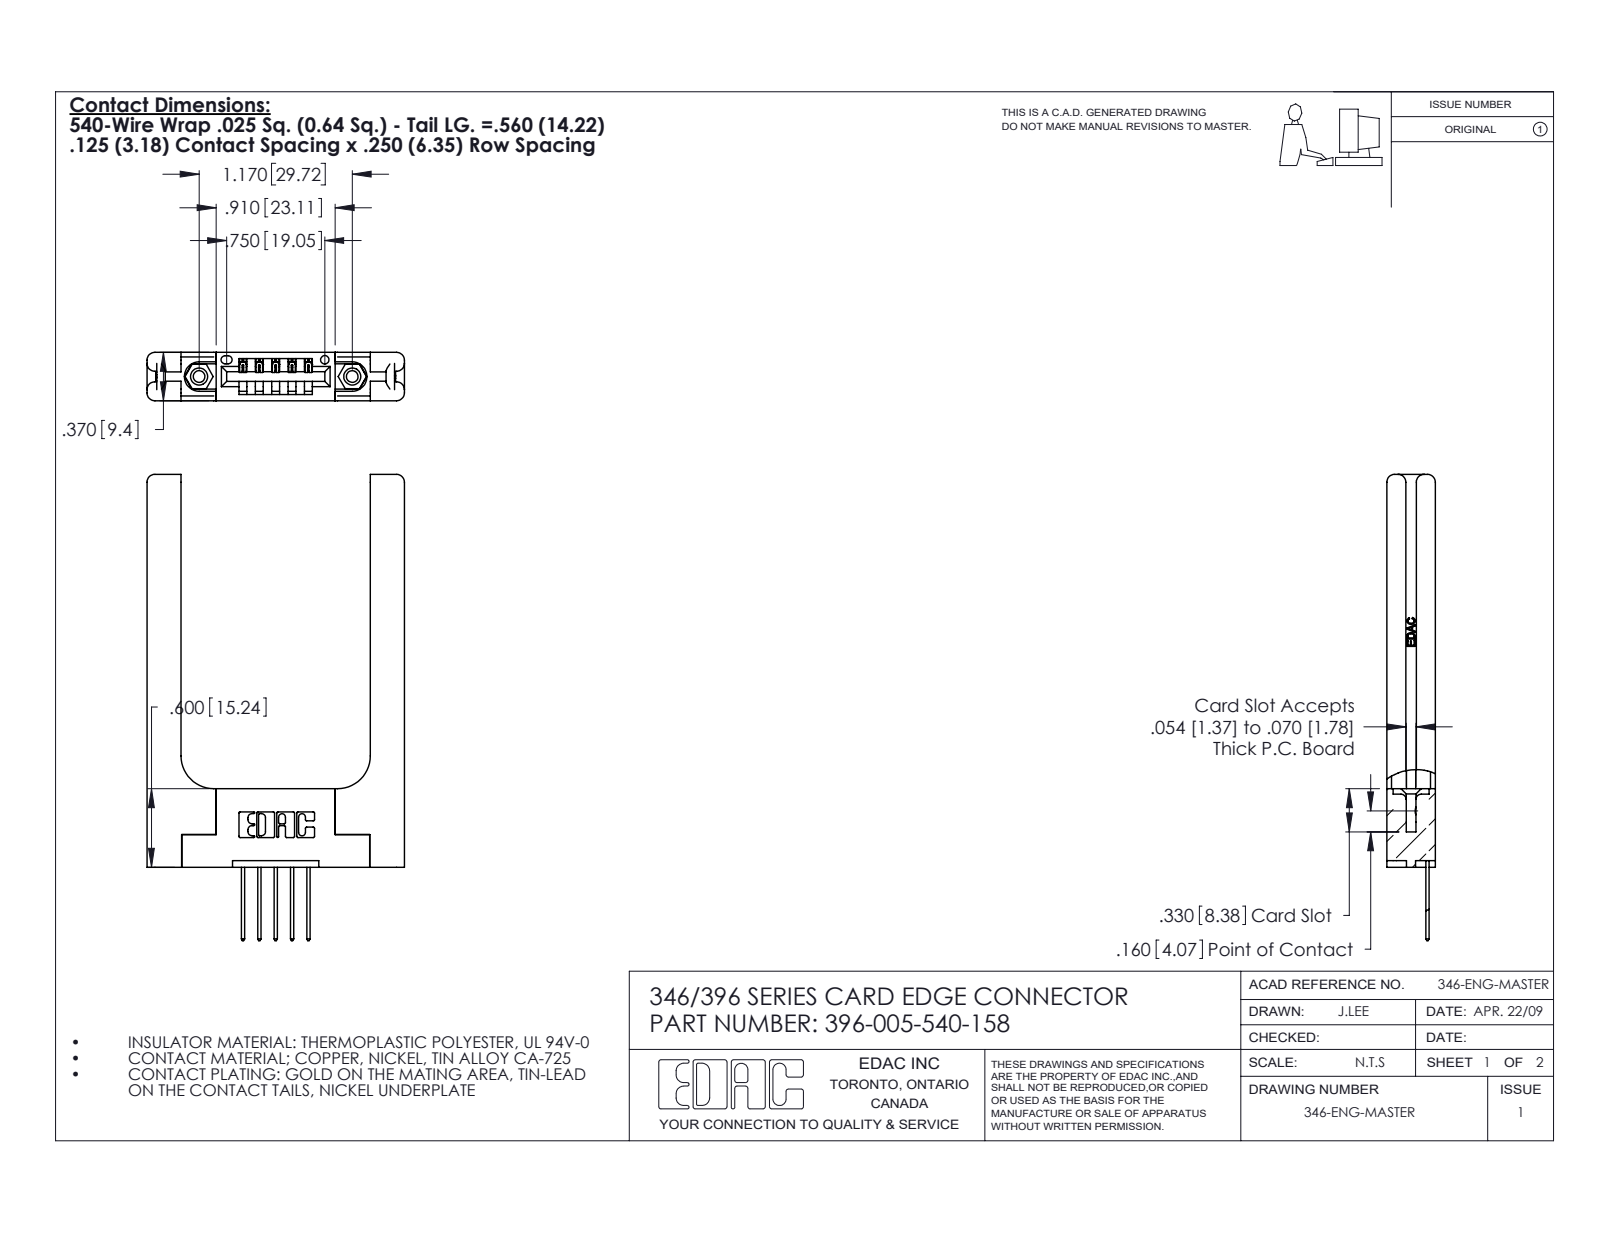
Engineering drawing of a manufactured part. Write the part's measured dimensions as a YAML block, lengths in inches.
part_name: "345-292-001_345-293-140; 346 Part_Flush Mounting Lugs - 0.156 Dia-TH; 346-220-058_345-220-058; 396-005-540-158 (+1 more)"
step_written_by: "SolidWorks 2020 (CONFIG_CONTROL_DESIGN)"
units: inches
bodies: {solids: 10, faces: 682, planar: 438, cylindrical: 184, other: 60}
overall_size: [3.56, 1.966, 0.37]
volume: 0.734
surface_area: 16.27
round_holes:
  - {diameter: 0.089, count: 2}
  - {diameter: 0.125, count: 2}
  - {diameter: 0.156, count: 2}
  - {diameter: 0.064, count: 1}
round_bosses_or_shafts:
  - {diameter: 0.155, count: 2}
partial_cylinders:
  - {radius: 0.01, count: 22}
  - {radius: 0.06, count: 16}
  - {radius: 0.006, count: 10}
  - {radius: 0.01, count: 10}
  - {radius: 0.007, count: 6}
  - {radius: 0.031, count: 6}
  - {radius: 0.026, count: 3}
  - {radius: 0.03, count: 2}
face_to_face_distances: [0.37, 0.15, 0.22, 0.072, 0.25, 1.446, 0.148, 0.071, 0.26, 1.706]
hole_center_spacings: [0.246, 0.969, 1.17]
